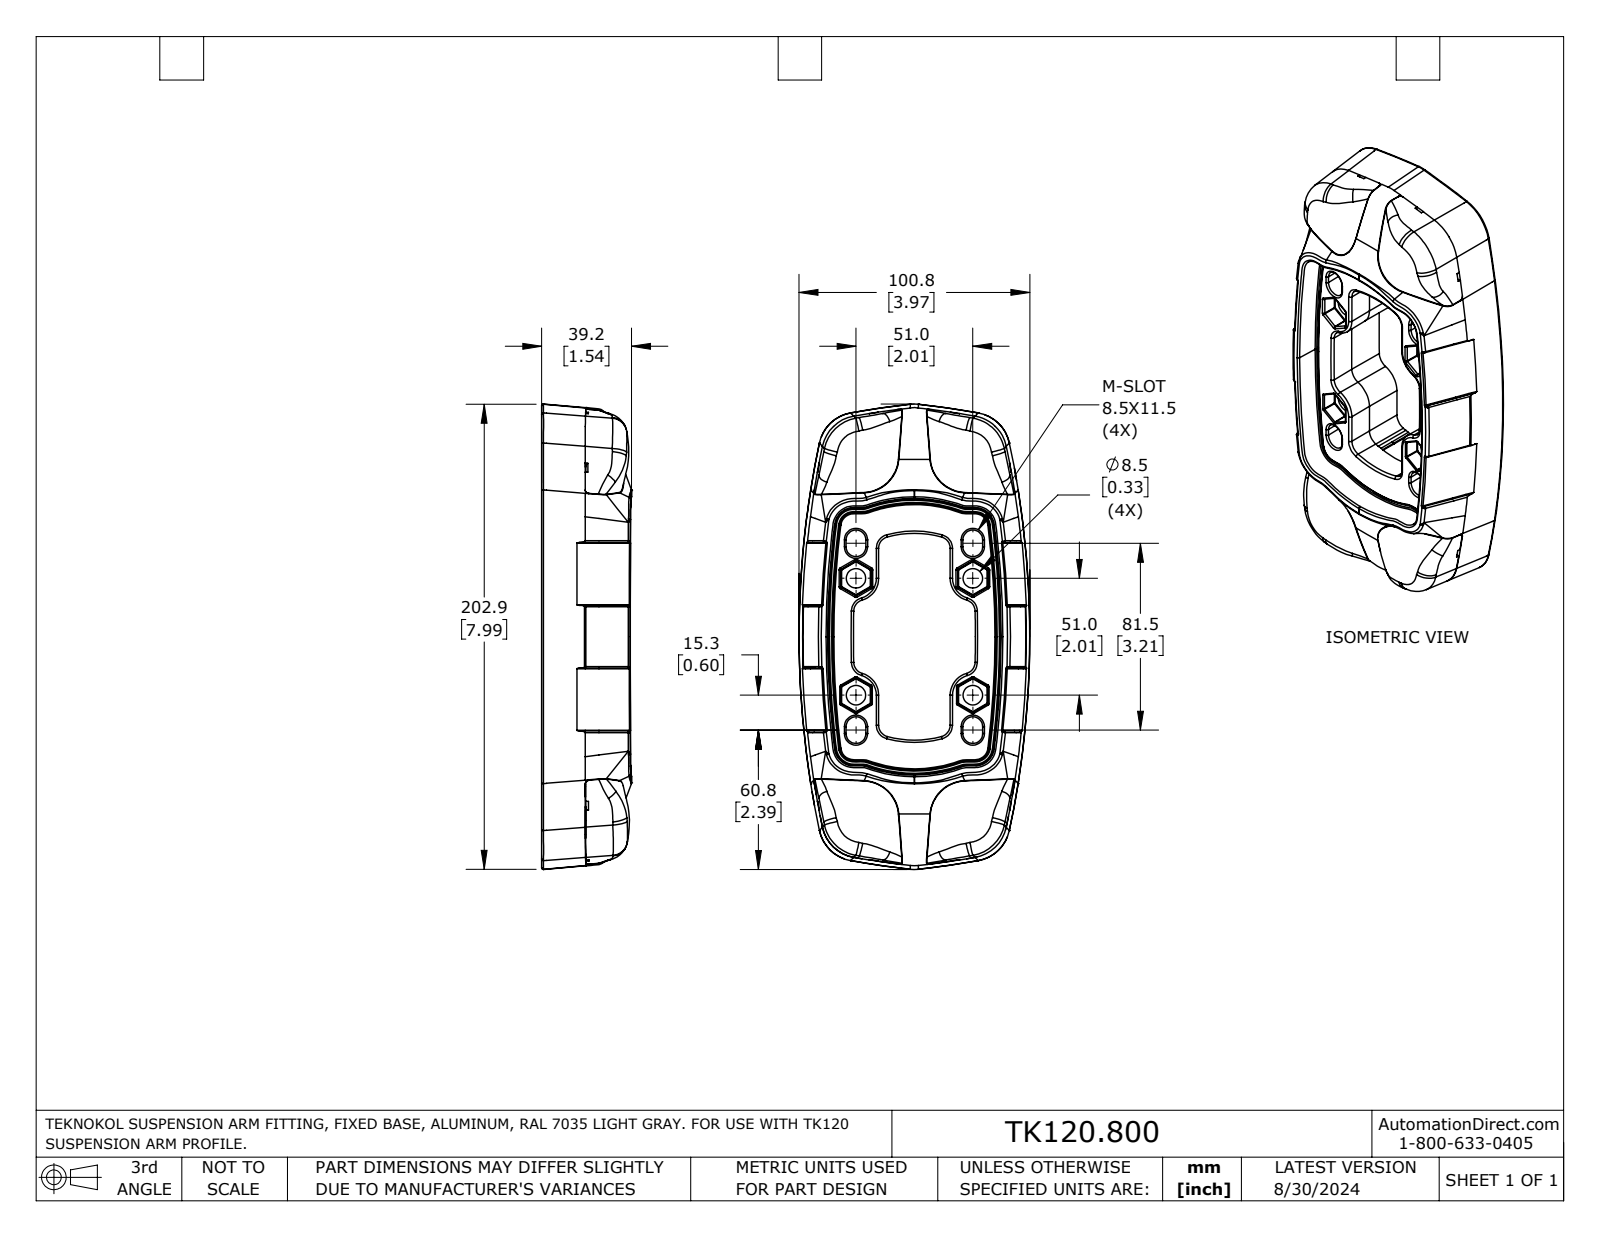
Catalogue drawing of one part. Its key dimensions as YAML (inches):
part_name: "TK120.800"
step_written_by: "SolidWorks 2023 (AUTOMOTIVE_DESIGN)"
units: inches
bodies: {solids: 1, faces: 683, planar: 123, cylindrical: 152, other: 408}
overall_size: [7.996, 3.966, 1.545]
volume: 22.47
surface_area: 124.1
round_holes:
  - {diameter: 0.177, count: 4}
  - {diameter: 0.339, count: 4}
round_bosses_or_shafts:
  - {diameter: 0.197, count: 8}
partial_cylinders:
  - {radius: 0.01, count: 44}
  - {radius: 0.029, count: 16}
  - {radius: 0.02, count: 12}
  - {radius: 0.069, count: 8}
  - {radius: 0.073, count: 8}
  - {radius: 0.209, count: 8}
  - {radius: 0.382, count: 4}
  - {radius: 1.949, count: 3}
face_to_face_distances: [1.141, 2.008, 1.244, 1.004, 1.112, 0.03, 0.876, 0.236, 0.266, 0.203]
hole_center_spacings: [2.008, 1.281, 1.691, 2.025, 2.618, 2.839, 2.883, 2.944]
